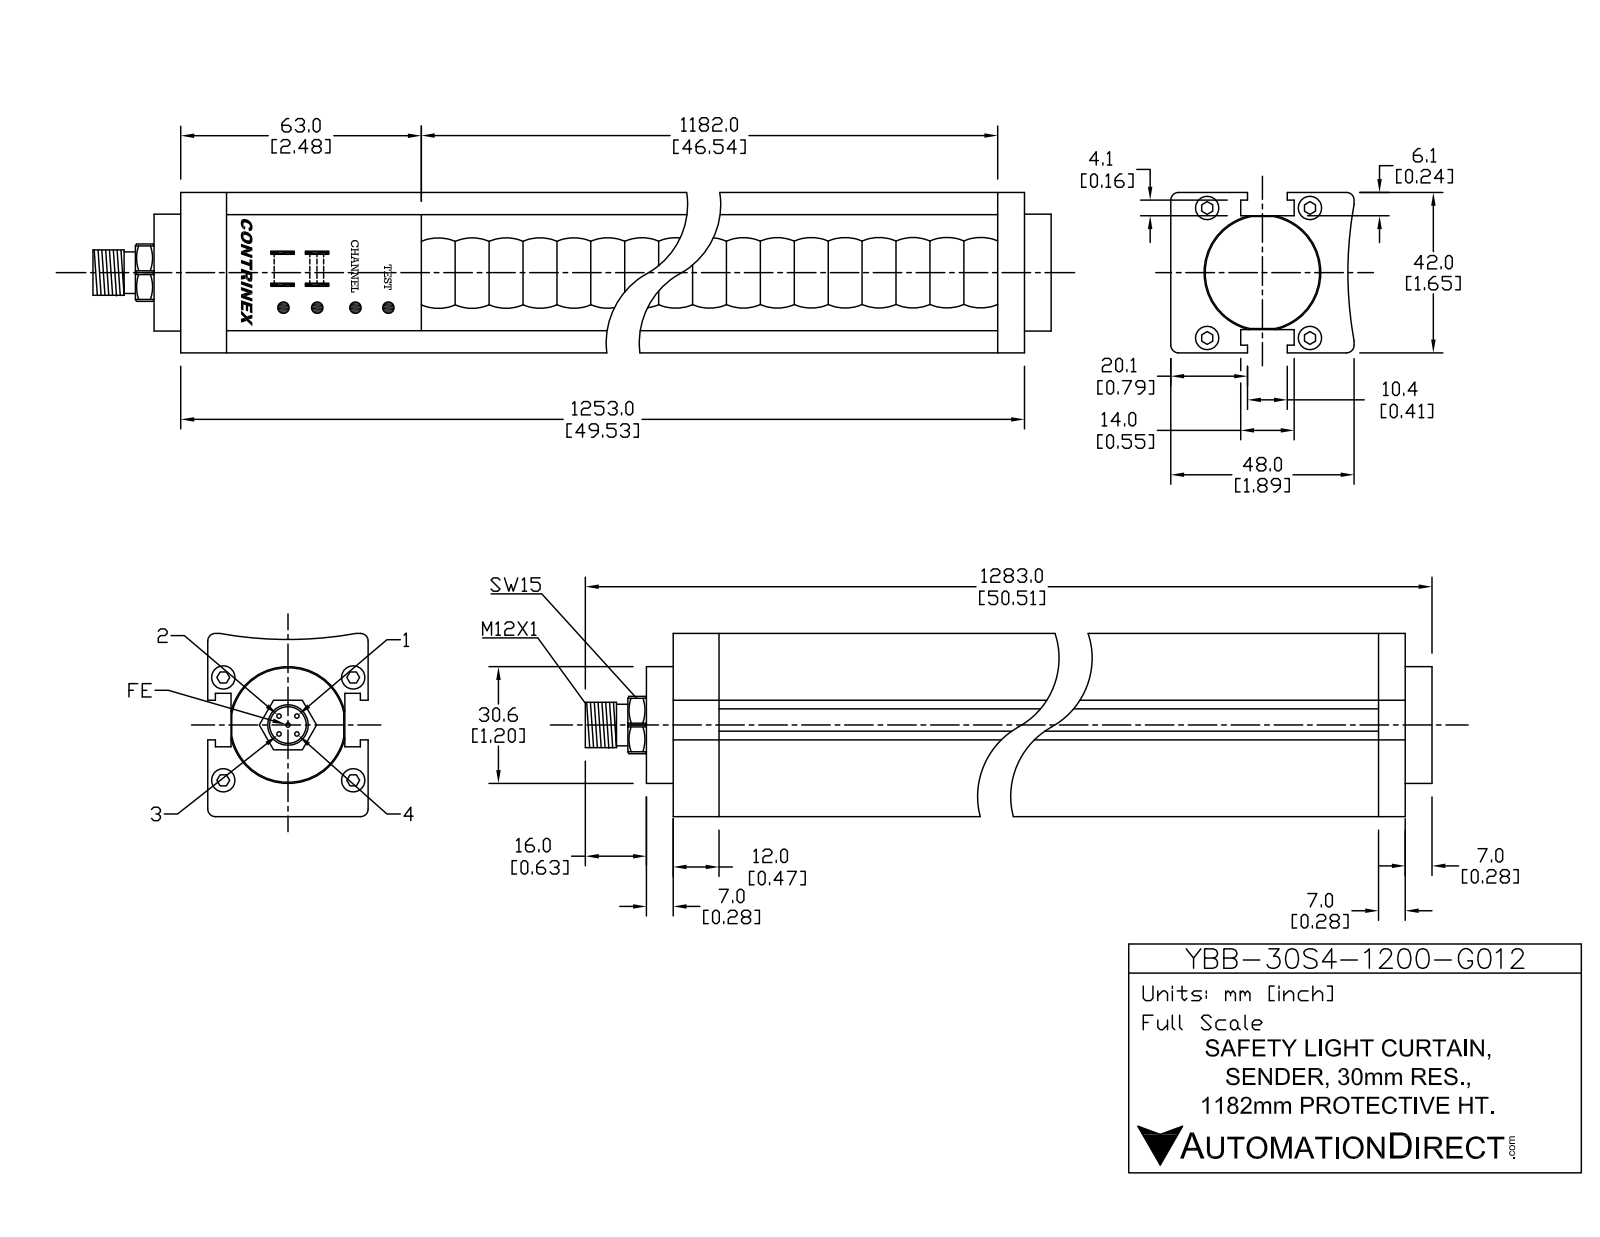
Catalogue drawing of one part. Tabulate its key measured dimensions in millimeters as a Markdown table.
| quantity | value |
| --- | --- |
| part name | YBB-30S4-1200-G012 |
| STEP written by | SolidWorks 2016 (AUTOMOTIVE_DESIGN) |
| units | millimeters |
| bodies | 19 solids, 440 faces (208 planar, 168 cylindrical, 64 other) |
| overall size | 1283 × 48 × 42 |
| volume | 2 253 000 mm³ |
| surface area | 284 832 mm² |
| round holes (diameter × count) | 6 × 4, 8.5 × 1, 32 × 1 |
| round bosses / shafts (diameter × count) | 1 × 5, 5.5 × 4, 30.6 × 1, 12 × 1, 10.5 × 1 |
| partial cylindrical surfaces (radius × count) | 1 × 48, 0.5 × 4, 0.55 × 2, 8.2 × 1, 100 × 1 |
| main face-to-face distances | 6.3, 35.7, 42, 29.4, 14, 17.2, 31.2, 15.7, 29.7, 46.9 |
| hole center spacings | 21.04, 22.34, 26.9, 34, 43.35 |
